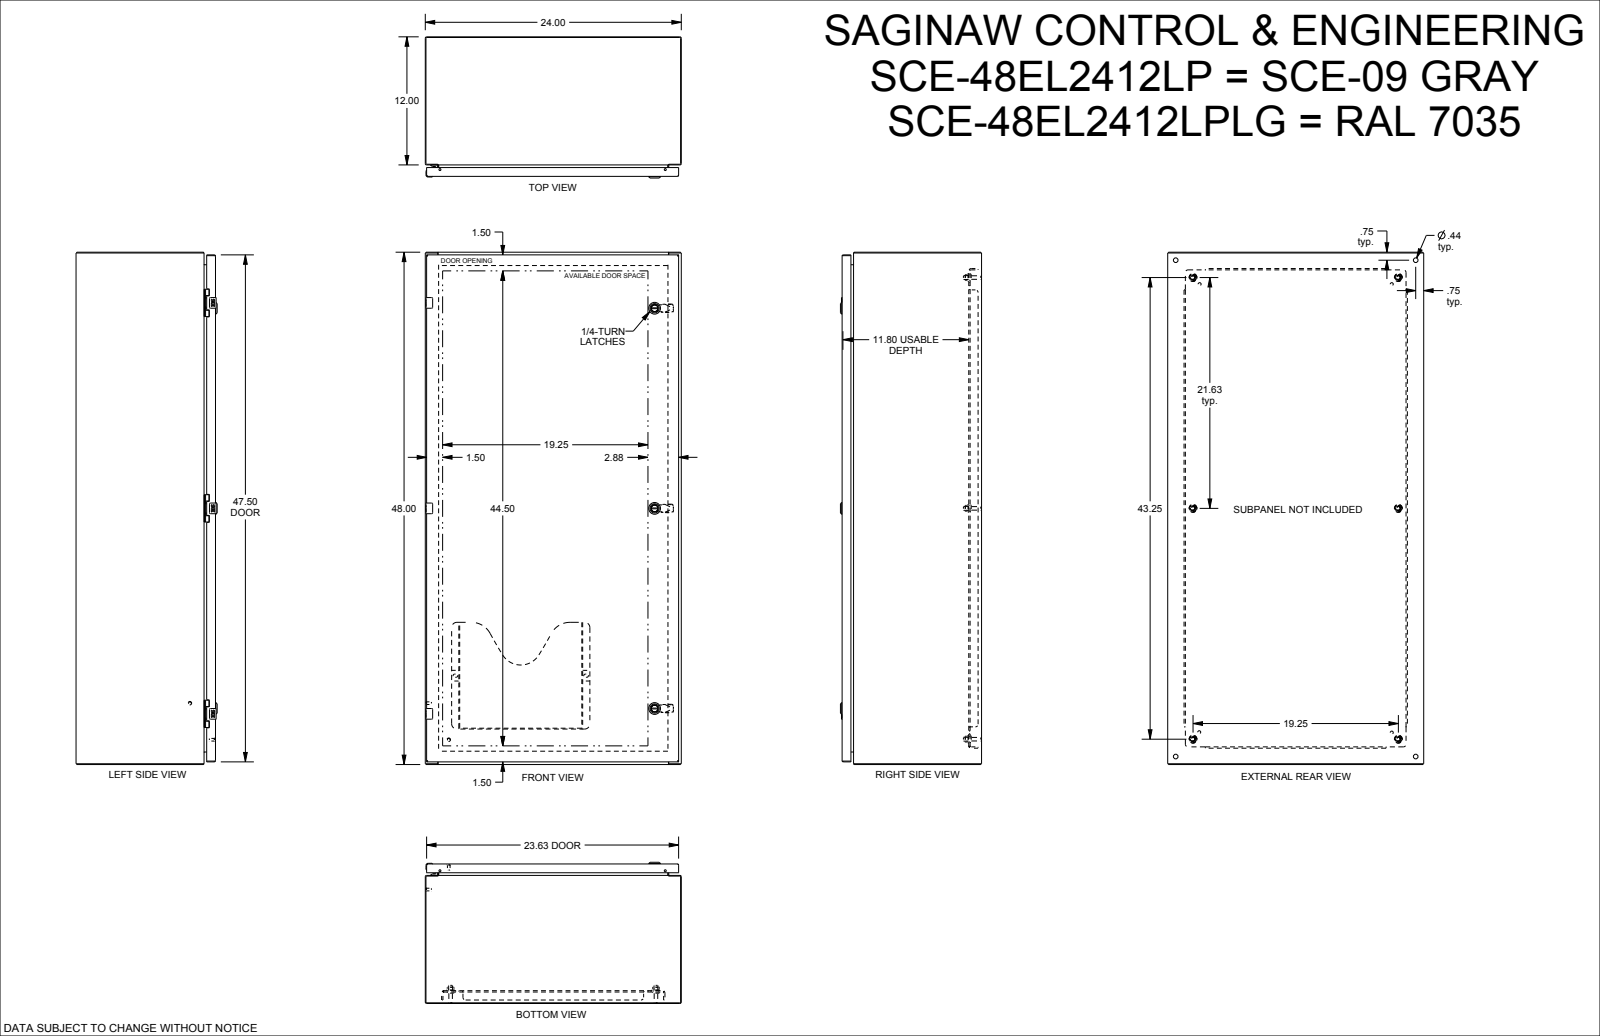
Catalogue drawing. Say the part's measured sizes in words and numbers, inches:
The part is named "SCE-48EL2412LP". Its 3-D file was written by "SolidWorks 2019 (CONFIG_CONTROL_DESIGN)". It is 0 solids with 3818 faces: 1807 planar, 1058 cylindrical and 953 other. Overall it measures 48 by 24 by 13.23 inches. Round holes: 6 of diameter 0.172, 6 of diameter 0.205, 6 of diameter 0.244, 6 of diameter 0.266, 6 of diameter 0.367, 6 of diameter 0.375, 6 of diameter 0.5, 4 of diameter 0.281, 4 of diameter 0.437, 3 of diameter 0.04, 3 of diameter 0.156, 3 of diameter 0.197. Round bosses or shafts: 9 of diameter 0.17, 6 of diameter 0.366, 6 of diameter 0.332, 6 of diameter 0.25, 6 of diameter 0.24, 4 of diameter 0.248, 4 of diameter 0.196, 3 of diameter 1.102. Partial cylindrical surfaces (rounded edges, fillets, slot ends): 82 of radius 0.012, 40 of radius 0.01, 32 of radius 0.015, 28 of radius 0.02, 17 of radius 0.04, 16 of radius 0.025, 16 of radius 0.1, 15 of radius 0.03. The main face-to-face distances are 0.075, 0.075, 12.923, 12.998, 23.925, 13.073, 12.998, 1.2, 11.873, 0.125. The hole center spacings are 19.25, 0.985, 38.5, 0.02, 0.493, 0.494, 4.493, 18.265.
